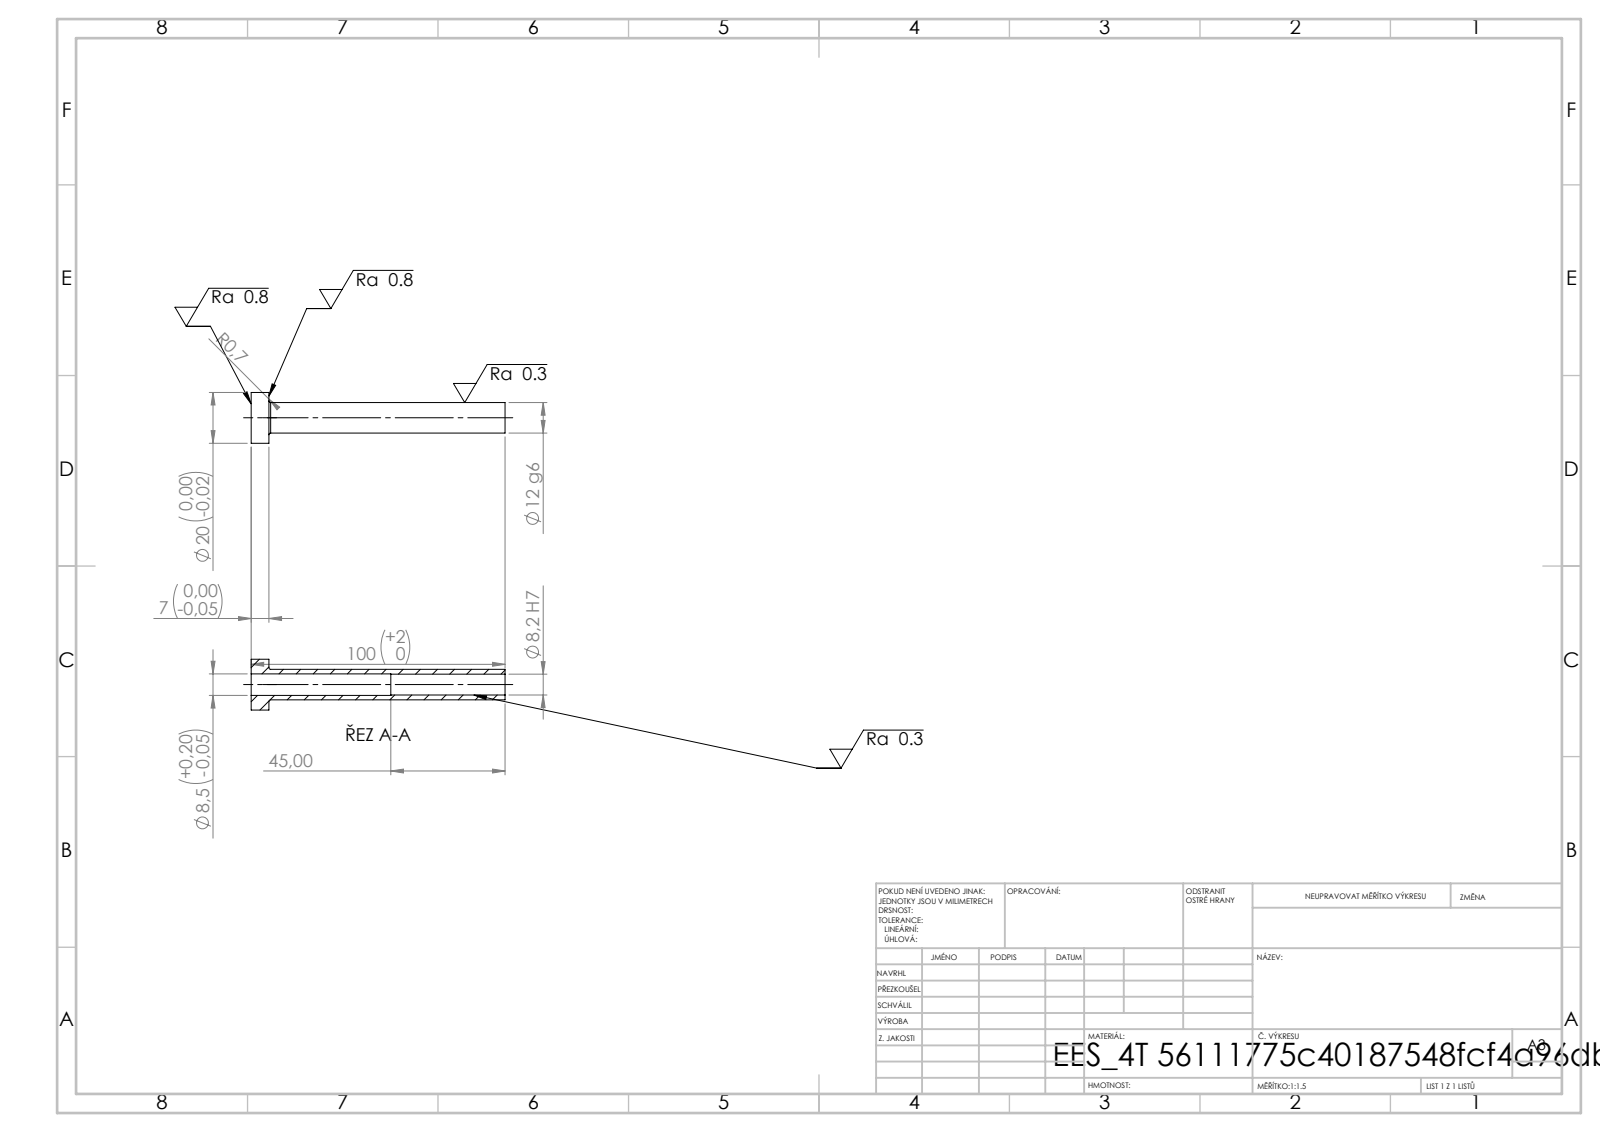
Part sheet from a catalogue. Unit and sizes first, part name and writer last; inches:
Units: inches
Overall size (bounding box): 3.937 × 0.787 × 0.787
Round holes (diameter × count): ⌀0.323 ×1, ⌀0.335 ×1
Round bosses / shafts (diameter × count): ⌀0.787 ×1, ⌀0.472 ×1
Main face-to-face distances: 0.276, 3.937, 3.661, 2.165, 1.89, 1.772
Volume: 0.441 in³ · Surface area: 10.98 in²
Bodies: 1 solid, 14 faces (4 planar, 8 cylindrical, 2 other)
STEP written by: SolidWorks 2019 (CONFIG_CONTROL_DESIGN)
